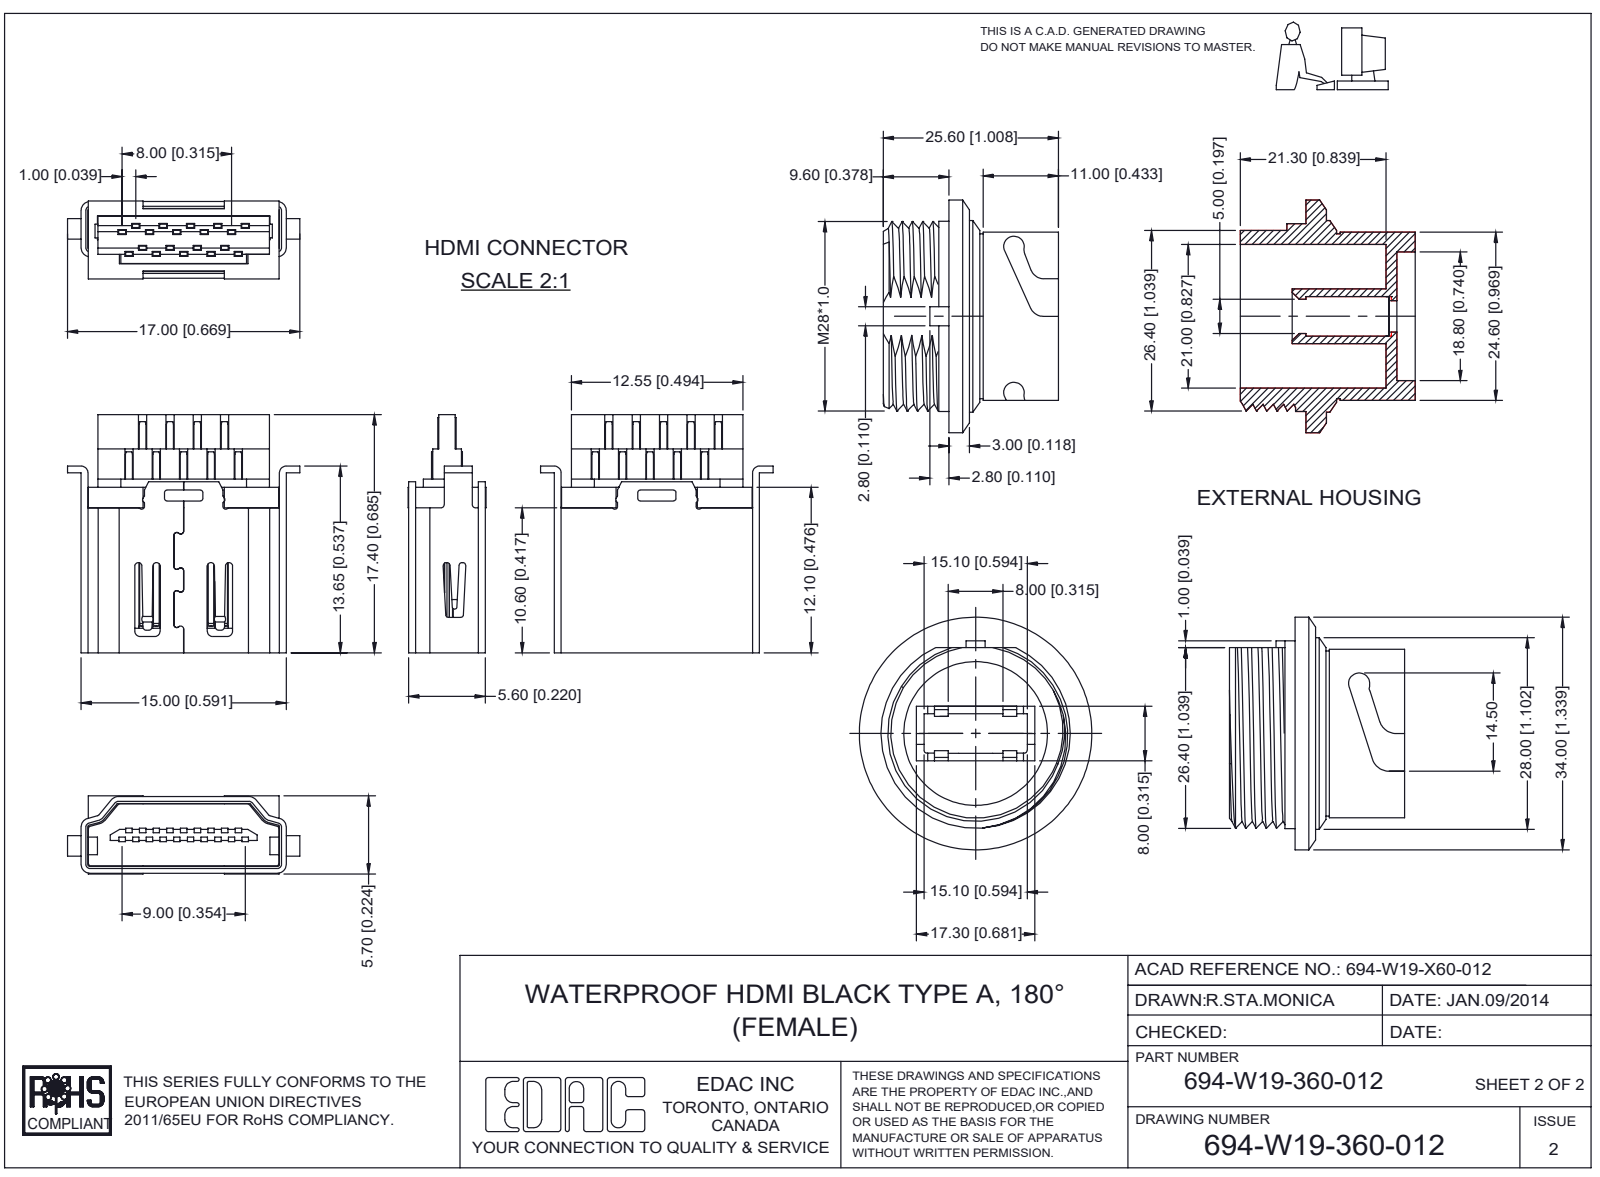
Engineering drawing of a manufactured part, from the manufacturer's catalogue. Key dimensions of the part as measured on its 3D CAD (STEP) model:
Part name (STEP PRODUCT): HDMI CONTACT2 694-W19-X60-012; HOUSING 694-W19-X60-012; HDMI HOUSING2 694-W19-X60-012; 694-W19-360-012 (+4 more)
STEP written by: SolidWorks 2020 (AUTOMOTIVE_DESIGN)
Units: millimetres
Bodies: 23 solids, 1962 faces (1365 planar, 542 cylindrical, 55 other)
Overall size (bounding box): 34 × 34 × 25.6
Volume: 7 371 mm³ · Surface area: 9 732 mm²
Round holes (diameter × count): ⌀18.8 ×1, ⌀21 ×1
Round bosses / shafts (diameter × count): ⌀34 ×1, ⌀28 ×1, ⌀27.8 ×1, ⌀24.6 ×1, ⌀24.1 ×1
Partial cylindrical surfaces — rounded edges, fillets, slot ends (radius × count): R0.15 ×240, R0.21 ×38, R0.2 ×28, R0.5 ×12, R0.25 ×10, R0.1 ×6, R0.35 ×6, R0.65 ×6
Main face-to-face distances: 2.7, 0.5, 1.1, 0.55, 6.9, 9.6, 3, 1.6, 1.9, 8
